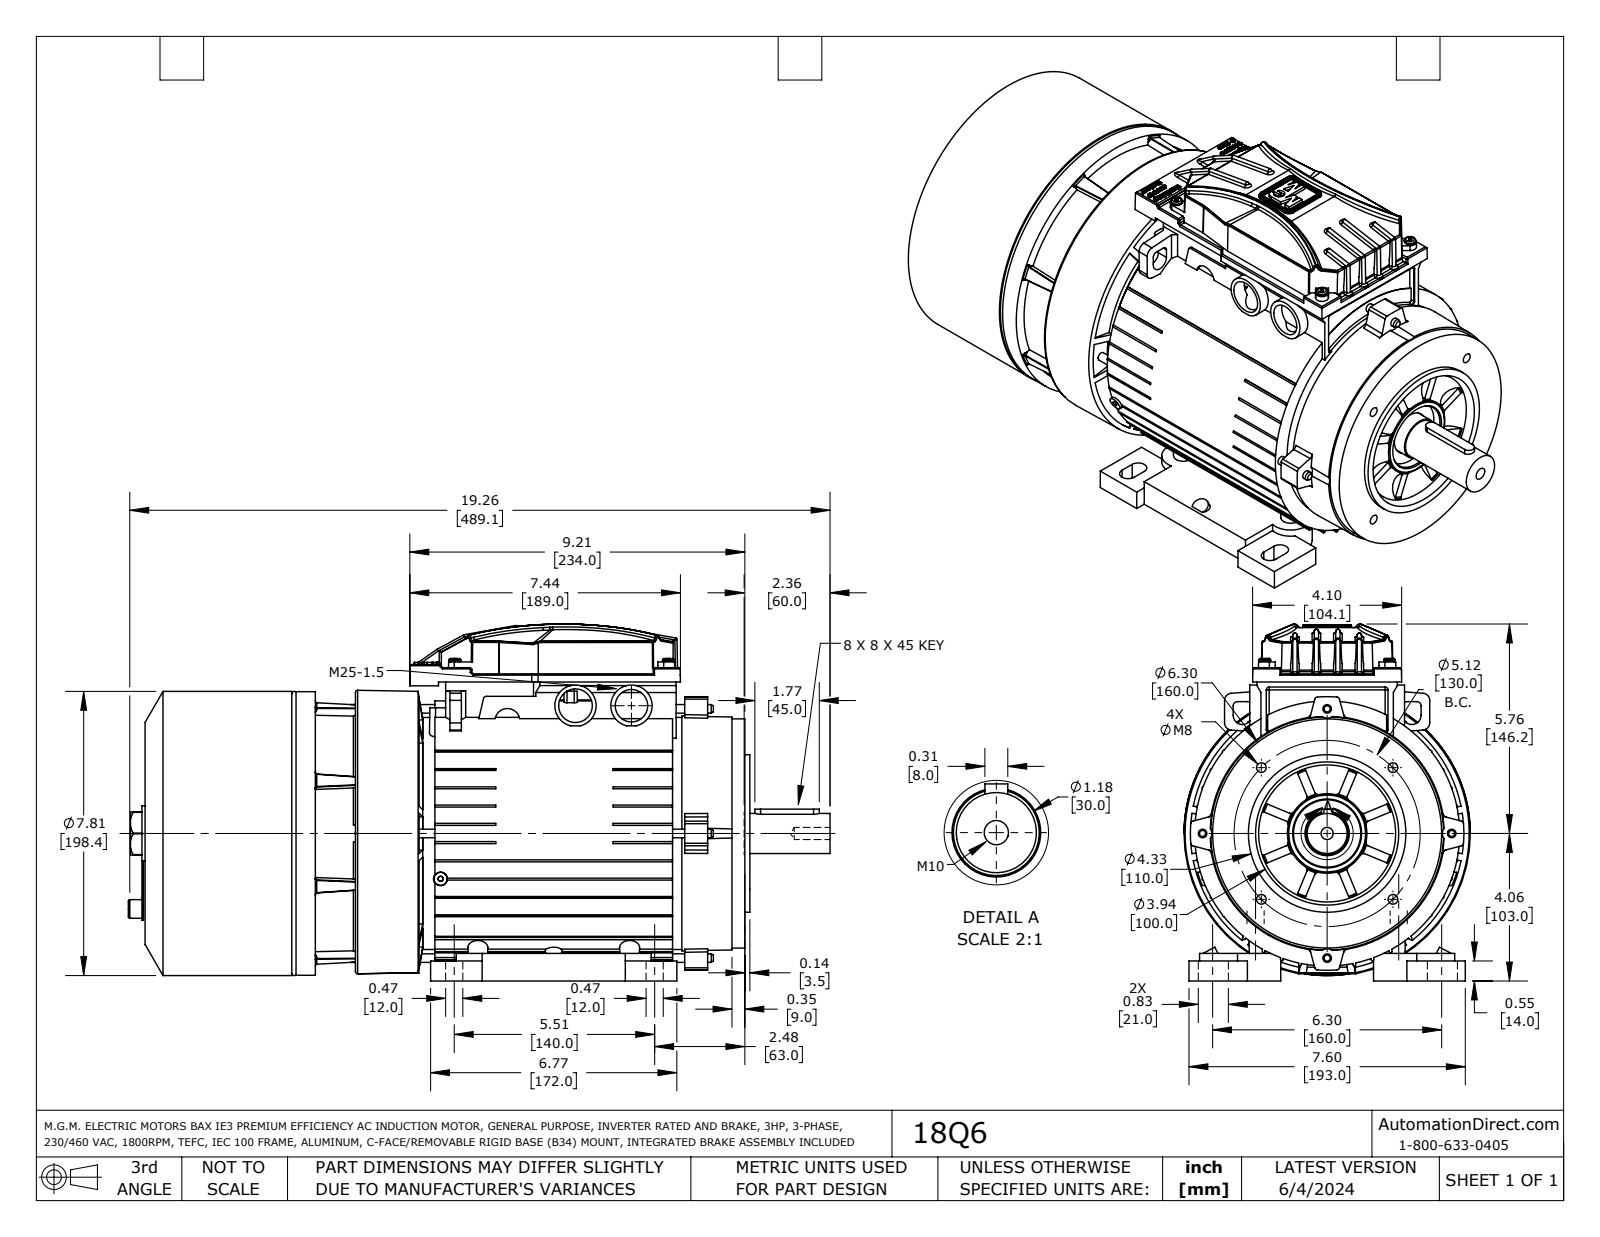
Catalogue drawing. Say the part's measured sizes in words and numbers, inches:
The part is named "18Q6". Its 3-D file was written by "SolidWorks 2021 (AUTOMOTIVE_DESIGN)". It is 11 solids with 3374 faces: 1344 planar, 868 cylindrical and 1162 other. Overall it measures 19.296 by 9.813 by 7.872 inches. Its volume is 661.3 cubic inches and its surface area 1 152 square inches. Round holes: 13 of diameter 0.13, 5 of diameter 0.098, 5 of diameter 0.335, 4 of diameter 0.15, 4 of diameter 0.177, 4 of diameter 0.268, 4 of diameter 0.531, 2 of diameter 0.118, 1 of diameter 0.472, 1 of diameter 0.512, 1 of diameter 0.894, 1 of diameter 0.925. Round bosses or shafts: 8 of diameter 0.315, 6 of diameter 0.138, 4 of diameter 0.522, 4 of diameter 0.236, 3 of diameter 0.276, 2 of diameter 1.138, 1 of diameter 7.811, 1 of diameter 7.795. Partial cylindrical surfaces (rounded edges, fillets, slot ends): 56 of radius 0.008, 49 of radius 0.059, 31 of radius 0.079, 24 of radius 0.004, 24 of radius 0.039, 22 of radius 0.02, 20 of radius 0.031, 16 of radius 0.033. The main face-to-face distances are 0.461, 7.97, 7.509, 6.791, 7.253, 14.762, 1.732, 8.524, 8.985, 16.494. The hole center spacings are 0.472, 0.818, 2.106, 2.25, 2.479, 2.559, 2.72, 2.912.
